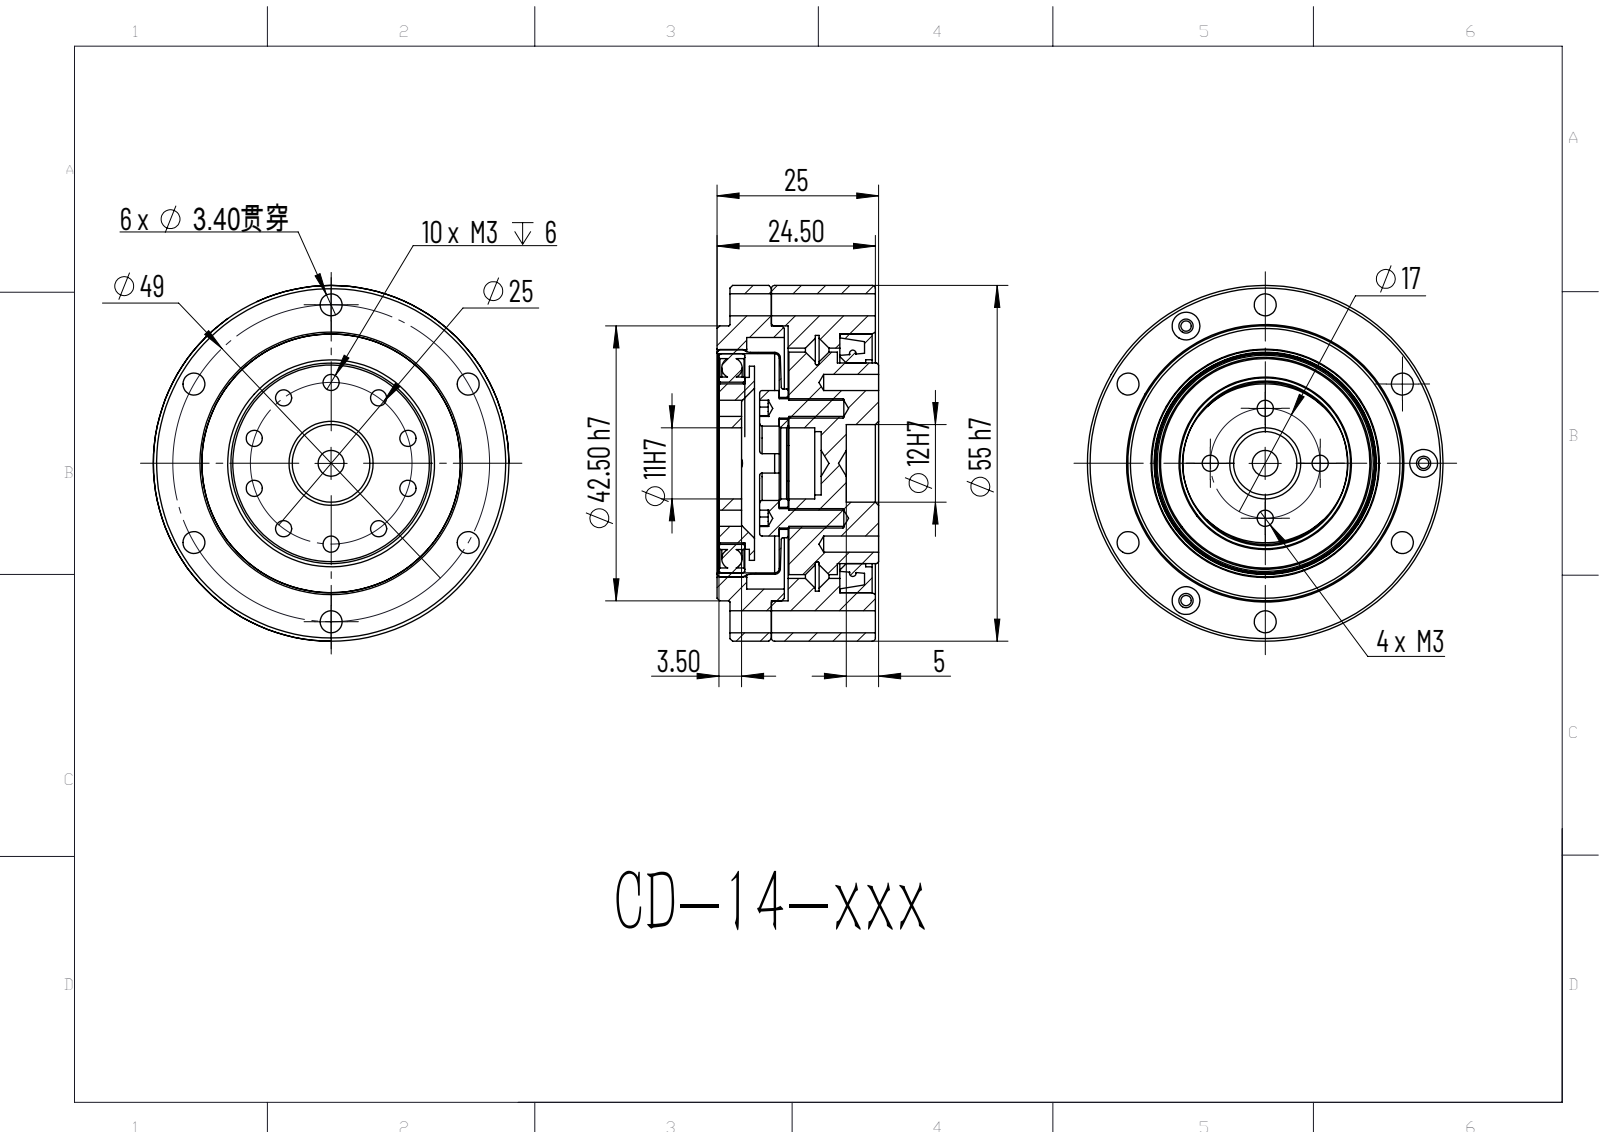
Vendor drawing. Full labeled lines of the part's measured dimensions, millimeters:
Part name (STEP PRODUCT): CD-14; 14-??; hexagon socket head cap screws gb_GB_FASTENER_SCREWS_HSHCS M3X10-N; 14-???? <1> (+5 more)
STEP written by: ONSHAPE BY PTC INC, 1.201 (AP242_MANAGED_MODEL_BASED_3D_ENGINEERING_MIM_LF)
Units: millimetres
Bodies: 17 solids, 384 faces (168 planar, 106 cylindrical, 110 other)
Overall size (bounding box): 55 × 55 × 25
Volume: 43 351 mm³ · Surface area: 32 136 mm²
Round holes (diameter × count): ⌀2.5 ×18, ⌀3.4 ×12, ⌀1.6 ×3, ⌀2.2 ×3, ⌀4.3 ×3, ⌀2.05 ×1, ⌀2.9 ×1, ⌀5 ×1, ⌀9.8 ×1, ⌀11 ×1, ⌀12 ×1, ⌀25.07 ×1
Round bosses / shafts (diameter × count): ⌀5.5 ×6, ⌀3 ×6, ⌀3.8 ×3, ⌀2 ×3, ⌀55 ×1, ⌀35.21 ×1, ⌀34.4 ×1, ⌀34.3 ×1
Main face-to-face distances: 1.2, 0.5, 2.6, 3.8, 6.4, 1.5, 22.5, 16.1, 7.6, 14.4
Hole centre spacings: 24.5, 8.5, 21.55, 29.68, 12.5, 17.66, 42.44, 25.93
